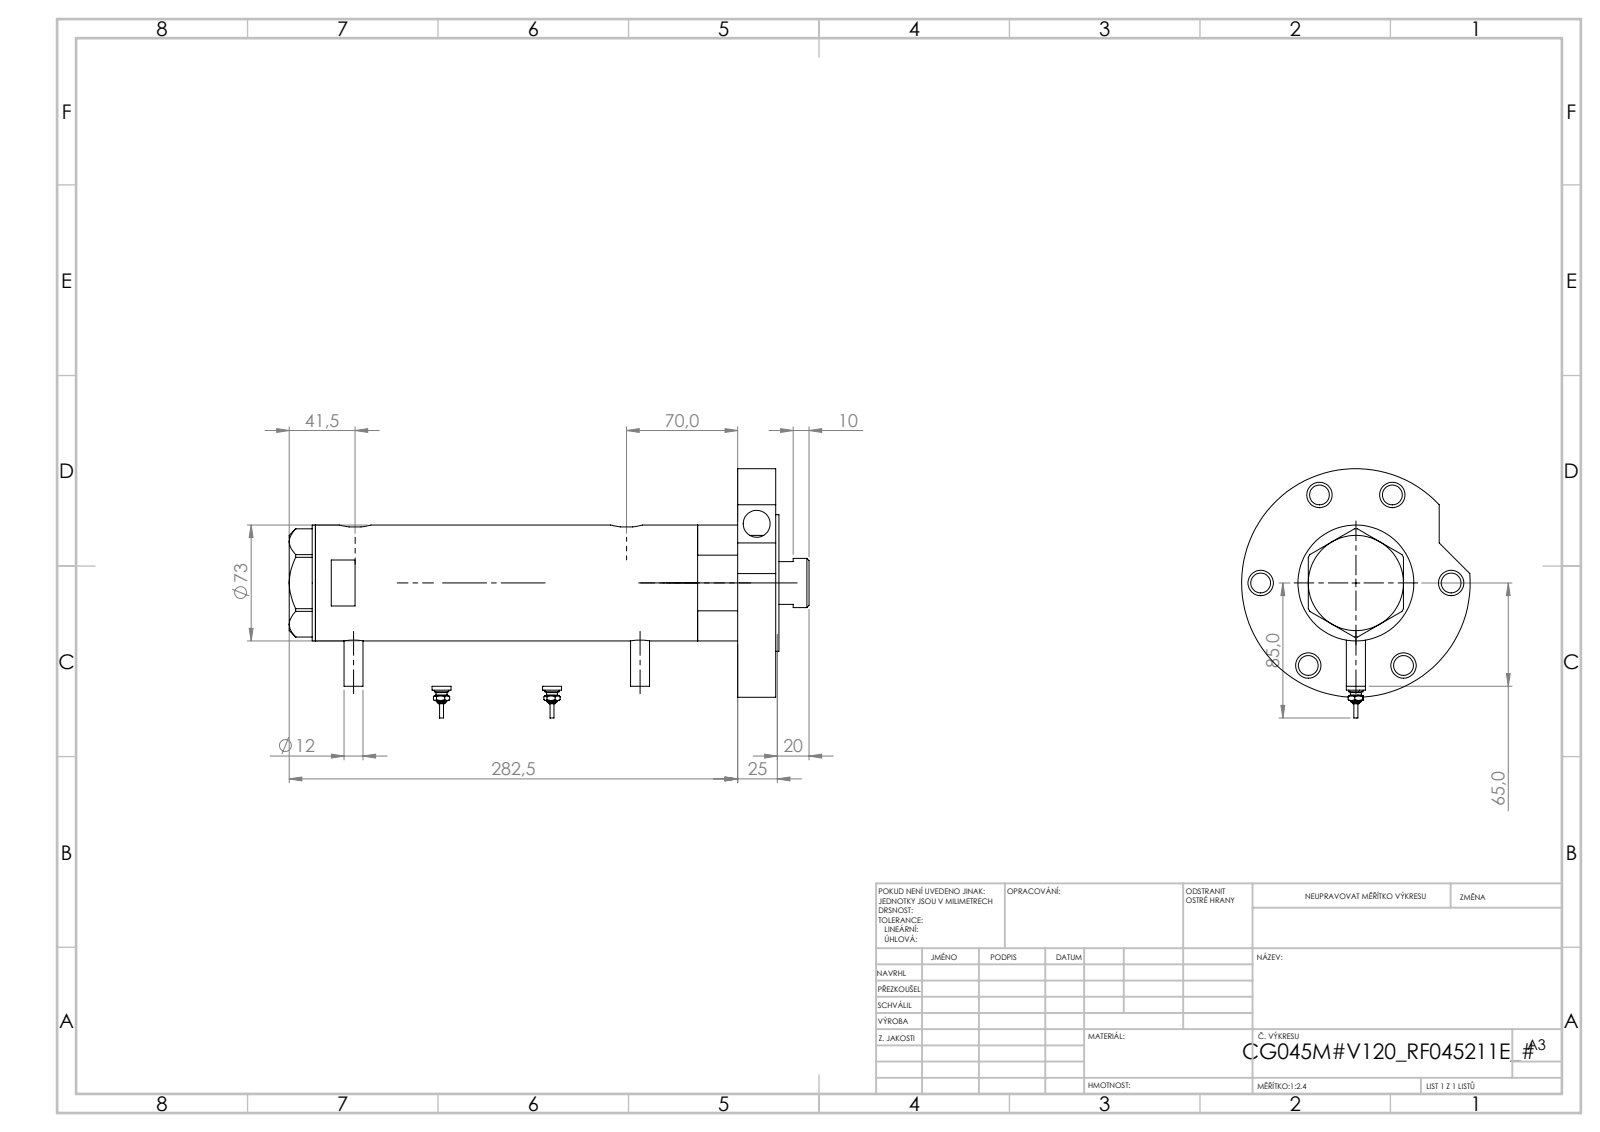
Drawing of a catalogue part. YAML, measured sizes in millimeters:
part_name: "V270CG_VC; V270CG_RF211E; V270CG_FRONT; V270CG_SWITCH (+2 more)"
step_written_by: "SolidWorks 2019 (CONFIG_CONTROL_DESIGN)"
units: millimeters
bodies: {solids: 7, faces: 275, planar: 89, cylindrical: 112, other: 74}
overall_size: [311.52, 144, 144]
volume: 1351000
surface_area: 230946
round_holes:
  - {diameter: 12.5, count: 8}
  - {diameter: 16, count: 6}
  - {diameter: 5, count: 2}
  - {diameter: 13.16, count: 2}
  - {diameter: 10.5, count: 1}
  - {diameter: 17, count: 1}
  - {diameter: 32, count: 1}
  - {diameter: 33.5, count: 1}
  - {diameter: 45, count: 1}
  - {diameter: 48, count: 1}
  - {diameter: 60, count: 1}
  - {diameter: 64, count: 1}
round_bosses_or_shafts:
  - {diameter: 12, count: 3}
  - {diameter: 9, count: 2}
  - {diameter: 7, count: 2}
  - {diameter: 4.34, count: 2}
  - {diameter: 2.4, count: 2}
  - {diameter: 144, count: 1}
  - {diameter: 86, count: 1}
  - {diameter: 73, count: 1}
partial_cylinders:
  - {radius: 10, count: 2}
face_to_face_distances: [24, 247.45, 26, 271.45, 2, 273.45, 187.14, 60.31, 84.31, 161.14]
hole_center_spacings: [60, 66.67, 99.77, 103.92, 107.62, 119.74, 171.65, 0.99]
